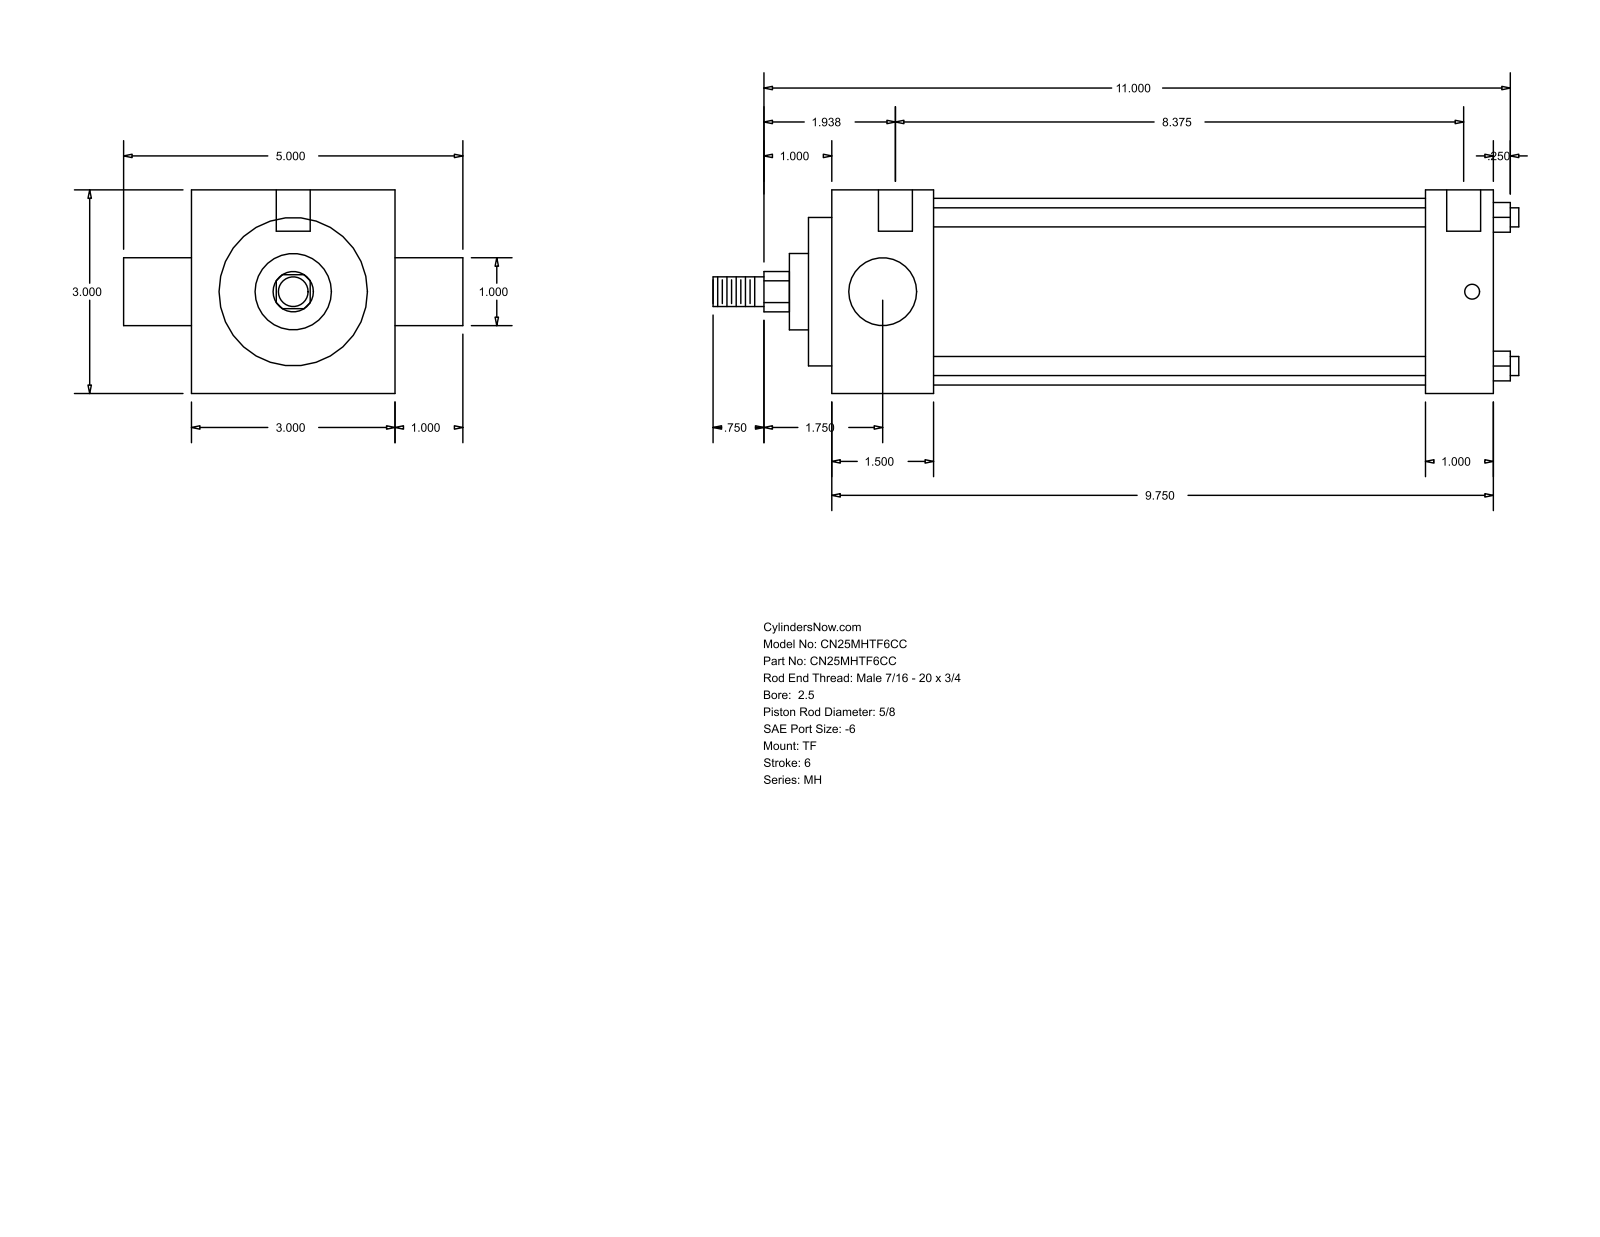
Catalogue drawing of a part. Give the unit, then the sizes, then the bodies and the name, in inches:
Units: inches
Overall size (bounding box): 11.875 × 5 × 3
Round holes (diameter × count): ⌀0.219 ×3, ⌀0.5 ×2
Round bosses / shafts (diameter × count): ⌀0.281 ×4, ⌀2.75 ×1, ⌀2.187 ×1, ⌀1.125 ×1, ⌀1 ×1, ⌀0.625 ×1, ⌀0.437 ×1
Partial cylindrical surfaces — rounded edges, fillets, slot ends (radius × count): R0.297 ×1
Main face-to-face distances: 3, 9.75, 1, 1.5, 8.25, 8.75, 7.25, 0.344, 1.844, 9.094
Hole centre spacings: 0.125, 0.187, 8.375, 8.5, 8.563, 8.687
Bodies: 0 solids, 86 faces (61 planar, 25 cylindrical, 0 other)
Part name (STEP PRODUCT): MH_TF__0250_0.625
STEP written by: GSSL Pune (CONFIG_CONTROL_DESIGN)
